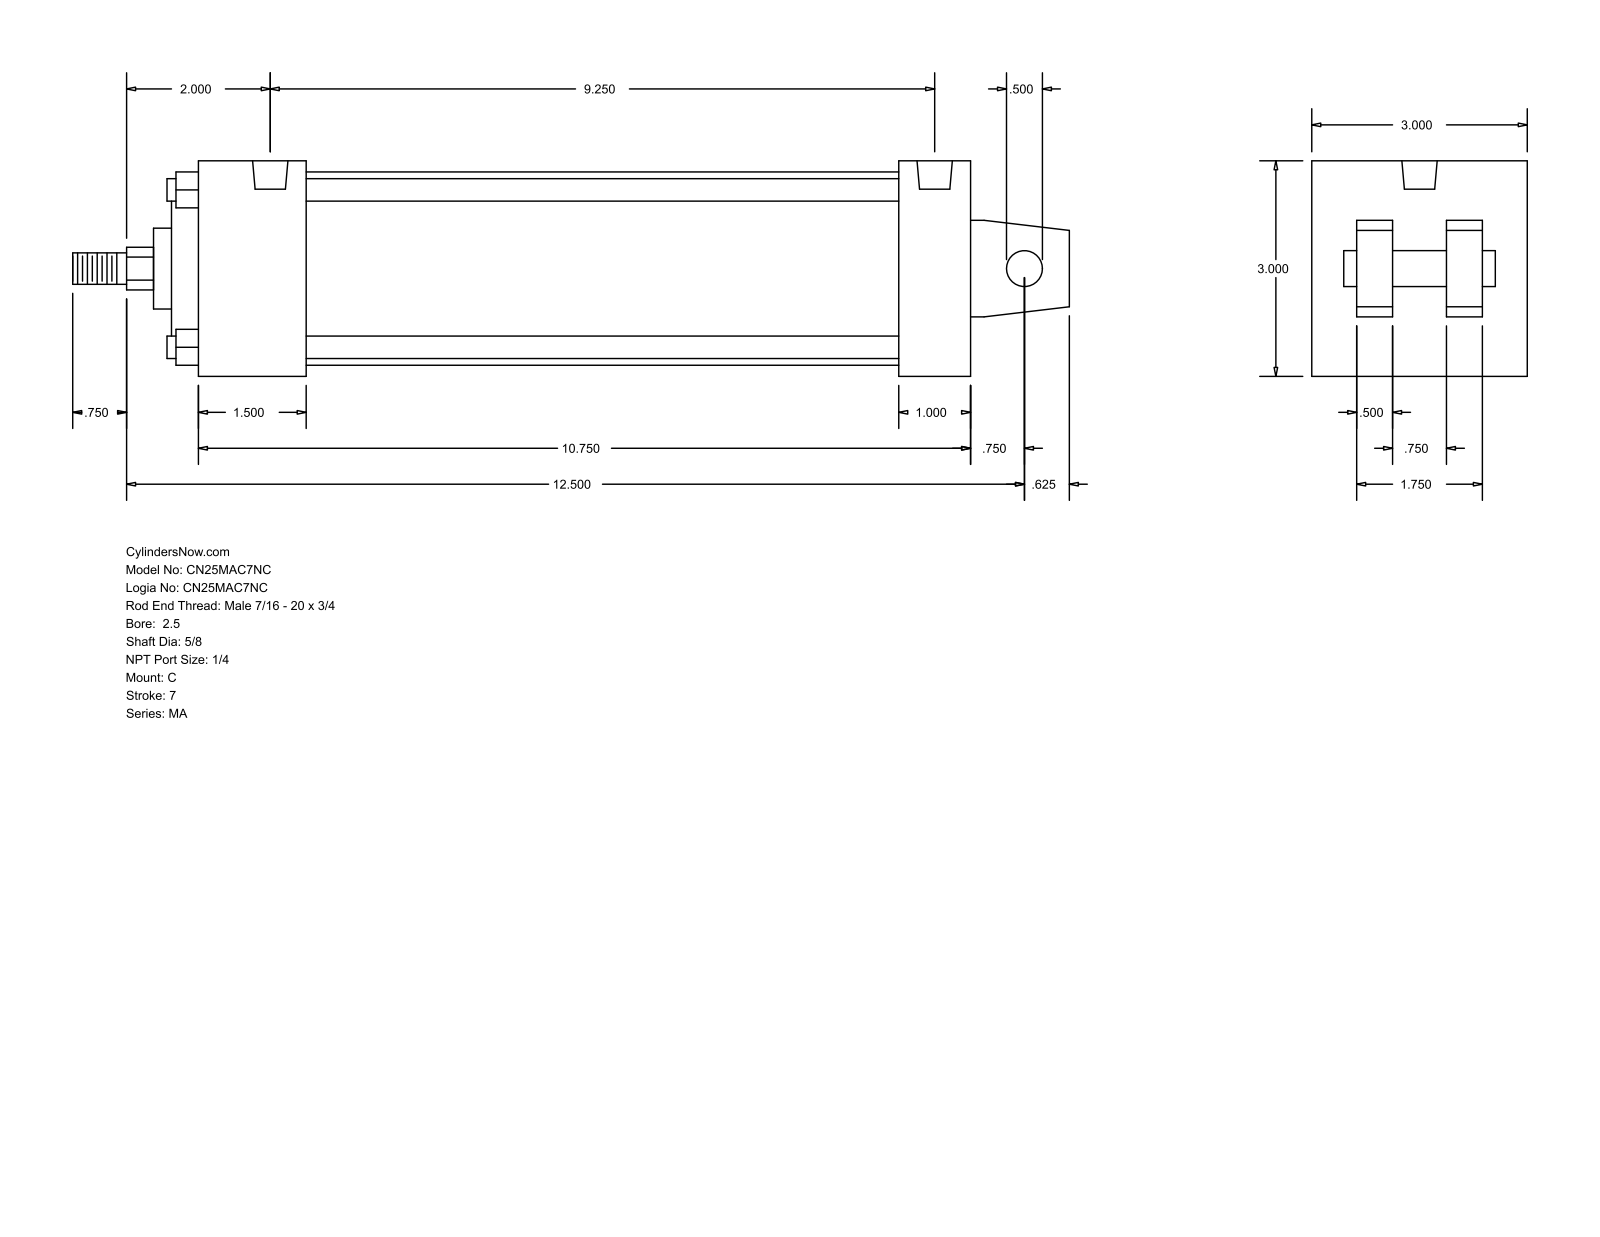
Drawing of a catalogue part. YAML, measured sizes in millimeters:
part_name: "MA_C__0250_0.625"
step_written_by: "GSSL Pune (CONFIG_CONTROL_DESIGN)"
units: millimeters
bodies: {solids: 0, faces: 105, planar: 77, cylindrical: 28, other: 0}
overall_size: [352.43, 76.2, 76.2]
round_holes:
  - {diameter: 7.94, count: 4}
  - {diameter: 12.49, count: 2}
round_bosses_or_shafts:
  - {diameter: 7.94, count: 4}
  - {diameter: 68.33, count: 1}
  - {diameter: 50.8, count: 1}
  - {diameter: 28.57, count: 1}
  - {diameter: 15.88, count: 1}
  - {diameter: 12.7, count: 1}
  - {diameter: 11.11, count: 1}
partial_cylinders:
  - {radius: 7.54, count: 1}
face_to_face_distances: [76.2, 273.05, 12.7, 15.87, 60.33, 47.63, 25.4, 38.1, 247.65, 209.55]
hole_center_spacings: [234.95]
